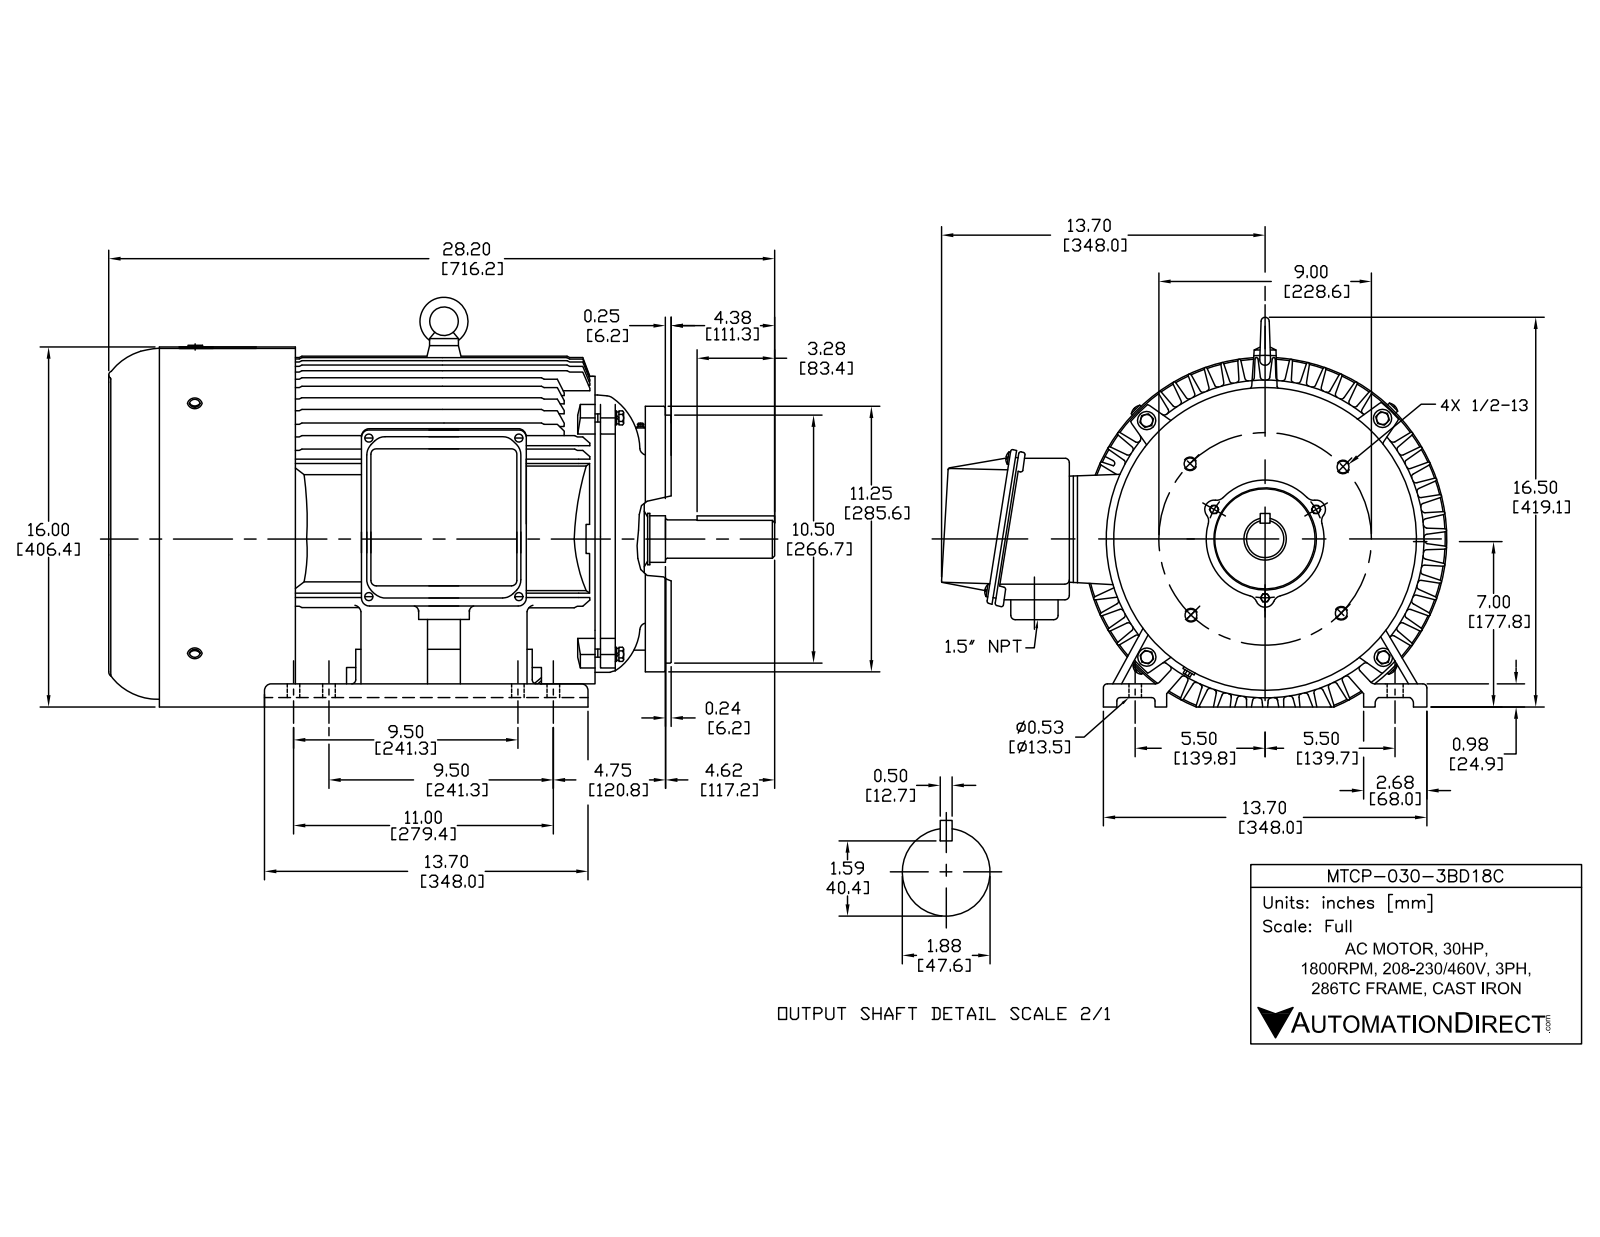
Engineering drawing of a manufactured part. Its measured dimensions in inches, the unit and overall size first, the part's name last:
Units: inches
Overall size (bounding box): 28.248 × 19.289 × 17.441
Round holes (diameter × count): ⌀0.276 ×14, ⌀0.394 ×10, ⌀0.197 ×8, ⌀0.669 ×8, ⌀0.252 ×4, ⌀0.263 ×4, ⌀0.268 ×4, ⌀0.354 ×4, ⌀0.402 ×4, ⌀0.422 ×4, ⌀0.448 ×4, ⌀0.508 ×4
Round bosses / shafts (diameter × count): ⌀0.472 ×8, ⌀0.236 ×8, ⌀0.315 ×6, ⌀0.945 ×4, ⌀0.752 ×4, ⌀0.389 ×4, ⌀0.197 ×4, ⌀0.394 ×2
Partial cylindrical surfaces — rounded edges, fillets, slot ends (radius × count): R0.039 ×273, R0.118 ×76, R0.197 ×74, R0.079 ×58, R0.02 ×48, R0.059 ×36, R0.315 ×26, R0.03 ×24
Main face-to-face distances: 0.059, 0.197, 0.472, 22.906, 22.846, 0.256, 0.394, 23.614, 23.555, 0.709
Hole centre spacings: 5.669, 3.937, 8.511, 2.559, 2.756, 4.604, 8.417, 2.663
Volume: 766.5 in³ · Surface area: 5 062 in²
Bodies: 68 solids, 4063 faces (1067 planar, 1440 cylindrical, 1556 other)
Part name (STEP PRODUCT): hex head bolts-full thread grade c gb_GB_FASTENER_BOLT_HHBFTC M5X16-N; hexagon head bolts-full thread gb_GB_FASTENER_BOLT_STBAB A M12X45-N; eyebolts gb_GB_FASTENER_SCREWS_FRS M16-N; PE280前轴承外盖加工件 (+8 more)
STEP written by: SolidWorks 2017 (AUTOMOTIVE_DESIGN)
